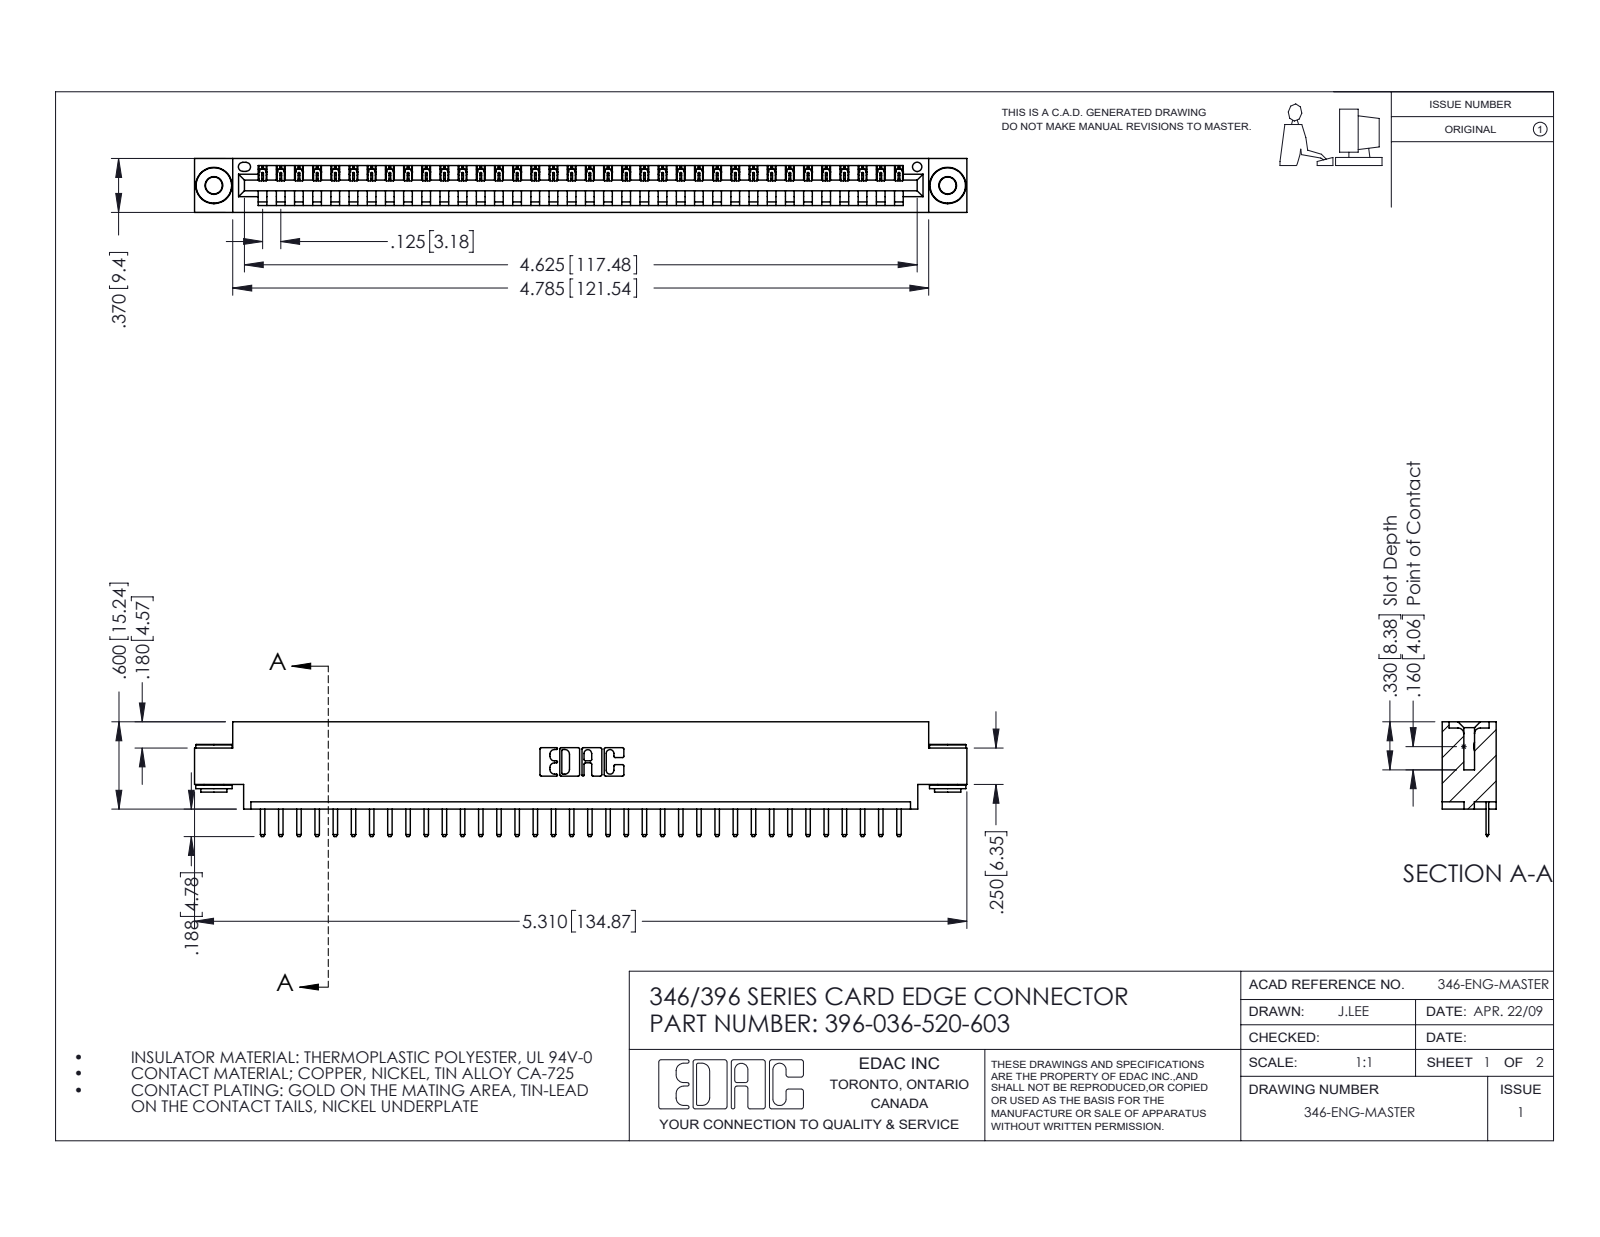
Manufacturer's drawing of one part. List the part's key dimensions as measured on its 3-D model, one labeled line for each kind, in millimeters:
Part name (STEP PRODUCT): 345-250-002_345-250-002-102; 396-036-520-603; 346 Part_0.170 Offset - 0.156 Dia-TH; 345-292-001_345-293-120
STEP written by: SolidWorks 2016 (CONFIG_CONTROL_DESIGN)
Units: millimetres
Bodies: 39 solids, 2396 faces (1602 planar, 786 cylindrical, 8 other)
Overall size (bounding box): 134.9 × 20 × 9.4
Volume: 12 600 mm³ · Surface area: 15 750 mm²
Round holes (diameter × count): ⌀2.9 ×2, ⌀4 ×2, ⌀1.6 ×1
Round bosses / shafts (diameter × count): ⌀6.4 ×2, ⌀4.6 ×2, ⌀3.5 ×2
Partial cylindrical surfaces — rounded edges, fillets, slot ends (radius × count): R0.3 ×74, R0.2 ×72, R0.3 ×22, R0.2 ×6, R0.8 ×6, R0.7 ×3, R0.8 ×2, R1 ×2
Main face-to-face distances: 1.2, 8.2, 9.4, 6.4, 0.6, 3.8, 5.6, 2.5, 4.4, 1.8
Hole centre spacings: 6.2, 122.8, 128.1
